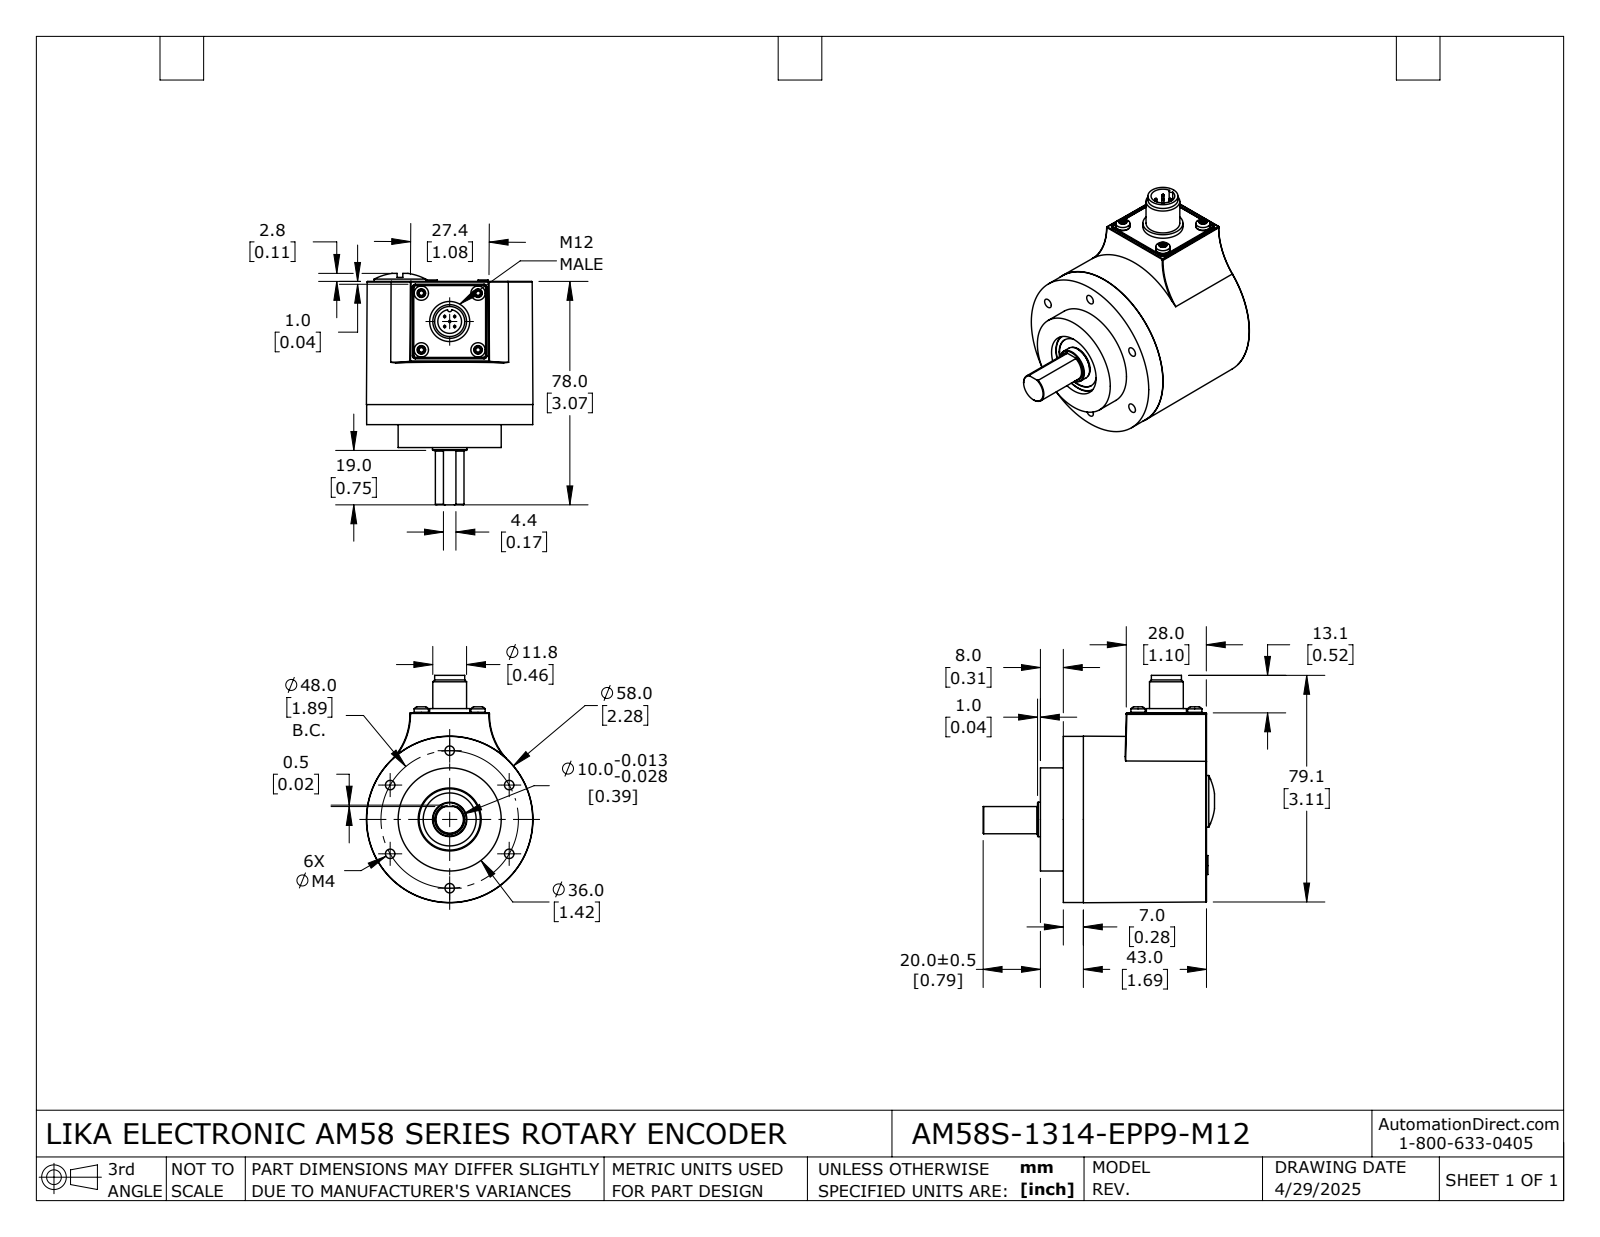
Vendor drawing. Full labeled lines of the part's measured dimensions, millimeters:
Part name (STEP PRODUCT): AM58S-1314-EPP9-M12
STEP written by: SolidWorks 2024 (AUTOMOTIVE_DESIGN)
Units: millimetres
Bodies: 40 solids, 1396 faces (371 planar, 483 cylindrical, 542 other)
Overall size (bounding box): 86.5 × 58 × 58
Volume: 61 320 mm³ · Surface area: 49 070 mm²
Round holes (diameter × count): ⌀2 ×11, ⌀1.2 ×10, ⌀3.3 ×6, ⌀2.1 ×5, ⌀3.5 ×5, ⌀1.6 ×4, ⌀2.5 ×4, ⌀12.5 ×3, ⌀9.7 ×2, ⌀10.9 ×2, ⌀1 ×1, ⌀3.2 ×1
Round bosses / shafts (diameter × count): ⌀1.6 ×12, ⌀1 ×12, ⌀3 ×6, ⌀13.3 ×3, ⌀12 ×2, ⌀58 ×1, ⌀55.5 ×1, ⌀55 ×1
Partial cylindrical surfaces — rounded edges, fillets, slot ends (radius × count): R0.2 ×26, R1 ×25, R3 ×3, R6.8 ×3, R7.6 ×3, R8.1 ×3, R9 ×3, R10 ×3
Main face-to-face distances: 2.5, 10, 40.5, 2, 43, 7, 5, 1, 3, 8
Hole centre spacings: 2.5, 3.5, 33.9, 5, 5.3, 7.5, 17, 20.1
